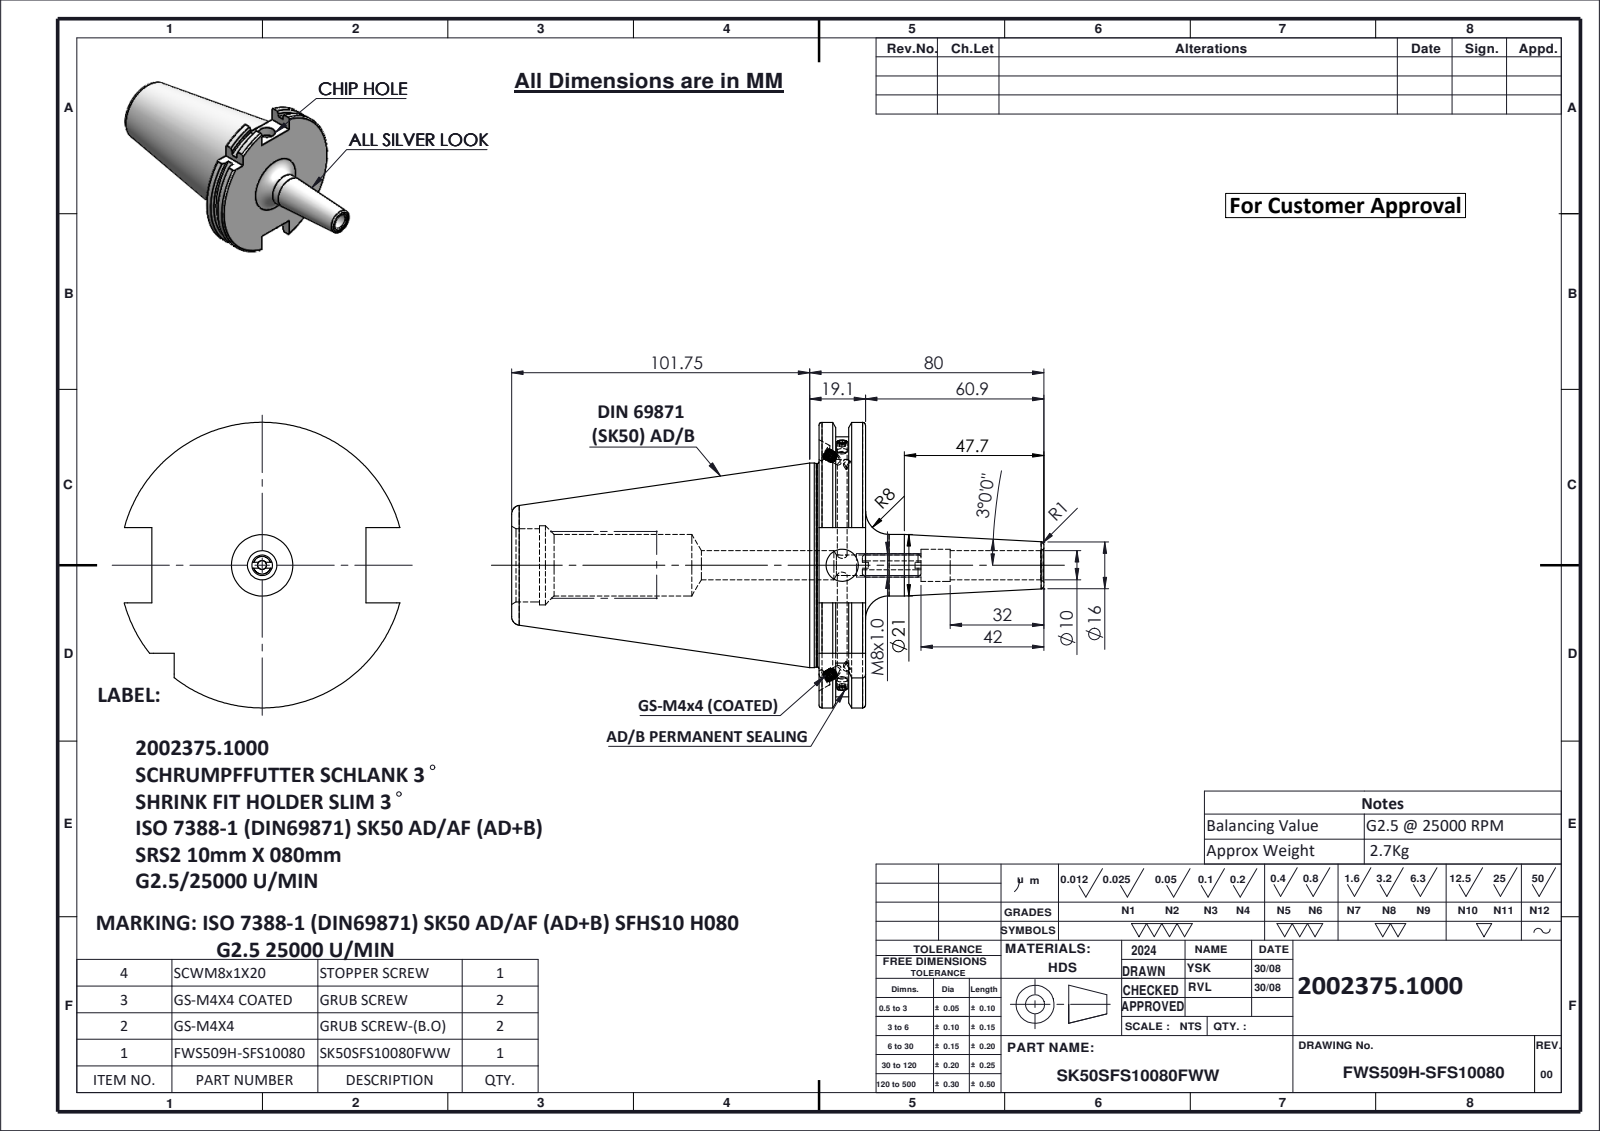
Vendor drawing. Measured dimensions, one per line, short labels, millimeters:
name: GS-M4X4-COATING_DIN 913 - M4 x 4-N; SK50SFS10080FWW; SCWM8X1; GS-M4X4_DIN 913 - M4 x 4-N (+1 more)
written by: SolidWorks 2024 (CONFIG_CONTROL_DESIGN)
unit: mm
bodies: 6 solids, 280 faces (79 planar, 81 cylindrical, 120 other)
size: 181.75 × 97.5 × 94.05
volume: 349 013 mm³; area: 49 478 mm²
holes: 2× ⌀3.2, 2× ⌀6, 2× ⌀11, 1× ⌀3, 1× ⌀3.3, 1× ⌀7, 1× ⌀10, 1× ⌀21, 1× ⌀25, 1× ⌀27
bosses: 4× ⌀4, 2× ⌀2.9, 1× ⌀69.85, 1× ⌀69.45, 1× ⌀8
rounds: 1× R44.9, 1× R48.75
face distances: 15.9, 5.65, 10.25, 10.14, 4.49, 5.76, 104.95, 110.6, 115.09, 120.85
